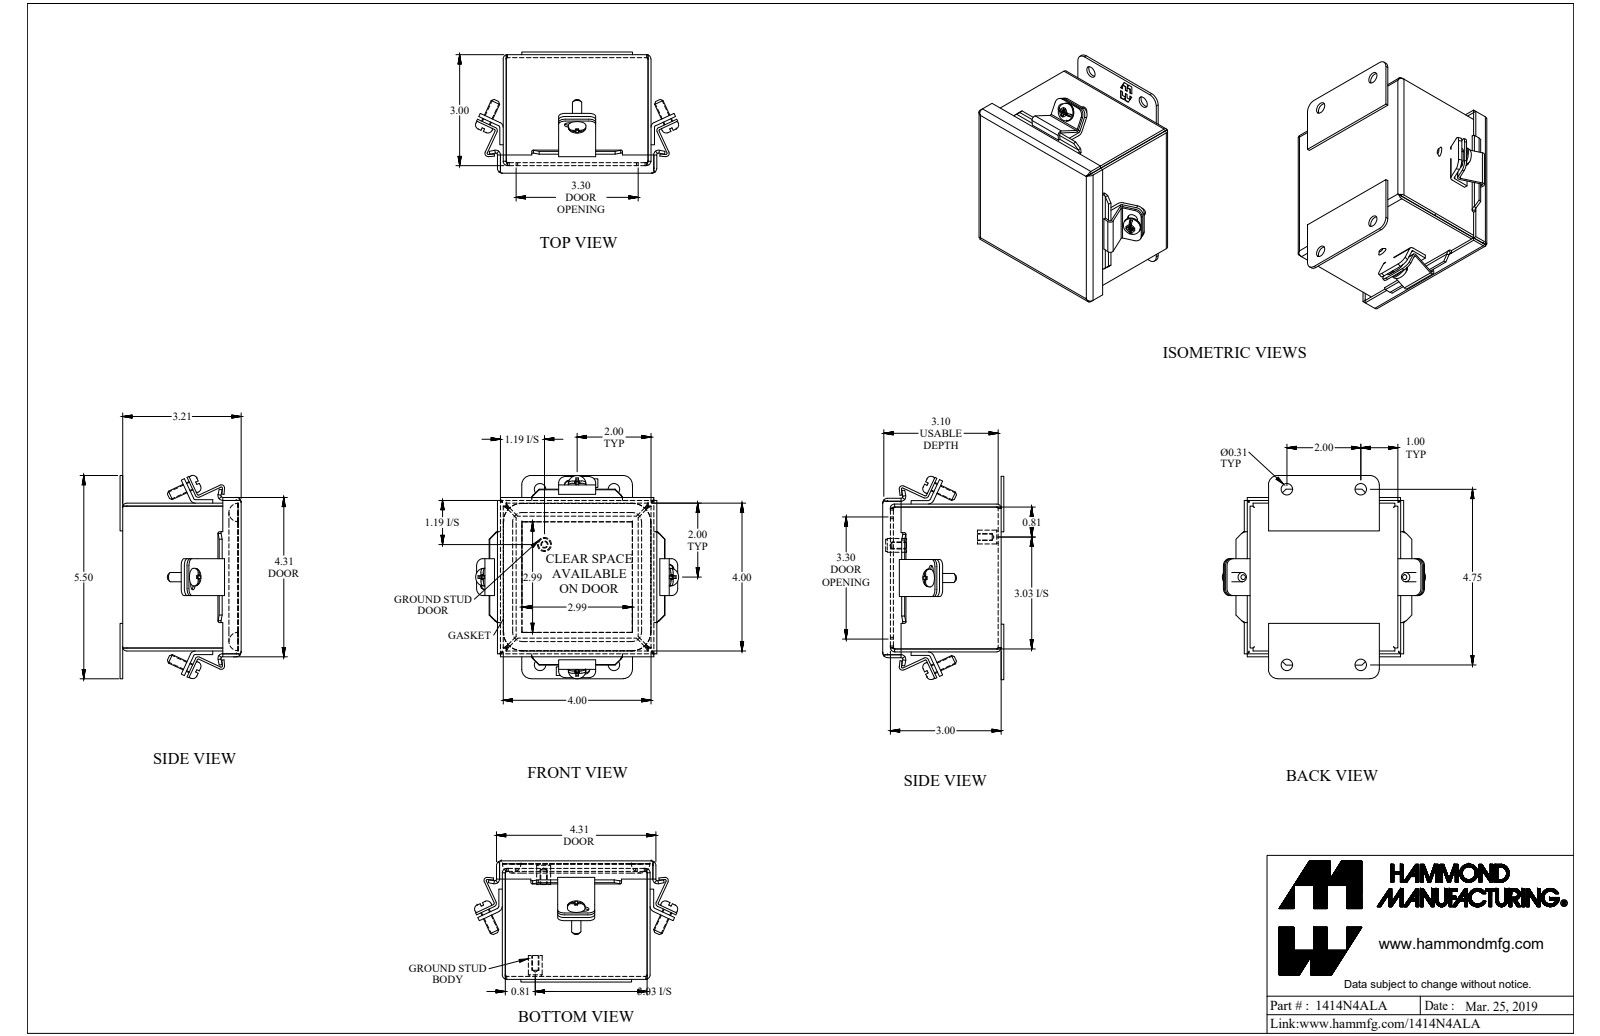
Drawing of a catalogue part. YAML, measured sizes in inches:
part_name: "1414N4ALA"
step_written_by: "SolidWorks 2018 (AUTOMOTIVE_DESIGN)"
units: inches
bodies: {solids: 19, faces: 652, planar: 436, cylindrical: 142, other: 74}
overall_size: [5.5, 5.497, 3.278]
volume: 10.41
surface_area: 267.5
round_holes:
  - {diameter: 0.213, count: 4}
  - {diameter: 0.313, count: 4}
  - {diameter: 0.159, count: 2}
round_bosses_or_shafts:
  - {diameter: 0.48, count: 4}
  - {diameter: 0.25, count: 4}
  - {diameter: 0.375, count: 2}
  - {diameter: 0.33, count: 2}
partial_cylinders:
  - {radius: 0.048, count: 12}
  - {radius: 0.01, count: 8}
  - {radius: 0.029, count: 8}
  - {radius: 0.036, count: 8}
  - {radius: 0.086, count: 8}
  - {radius: 0.117, count: 8}
  - {radius: 0.129, count: 8}
  - {radius: 0.141, count: 8}
face_to_face_distances: [0.081, 3.919, 3.125, 4, 3.838, 0.081, 3.206, 3.125, 3.044, 0.156]
hole_center_spacings: [2, 4.75, 5.154, 0.32, 1.272, 1.498, 2.402, 2.459]
